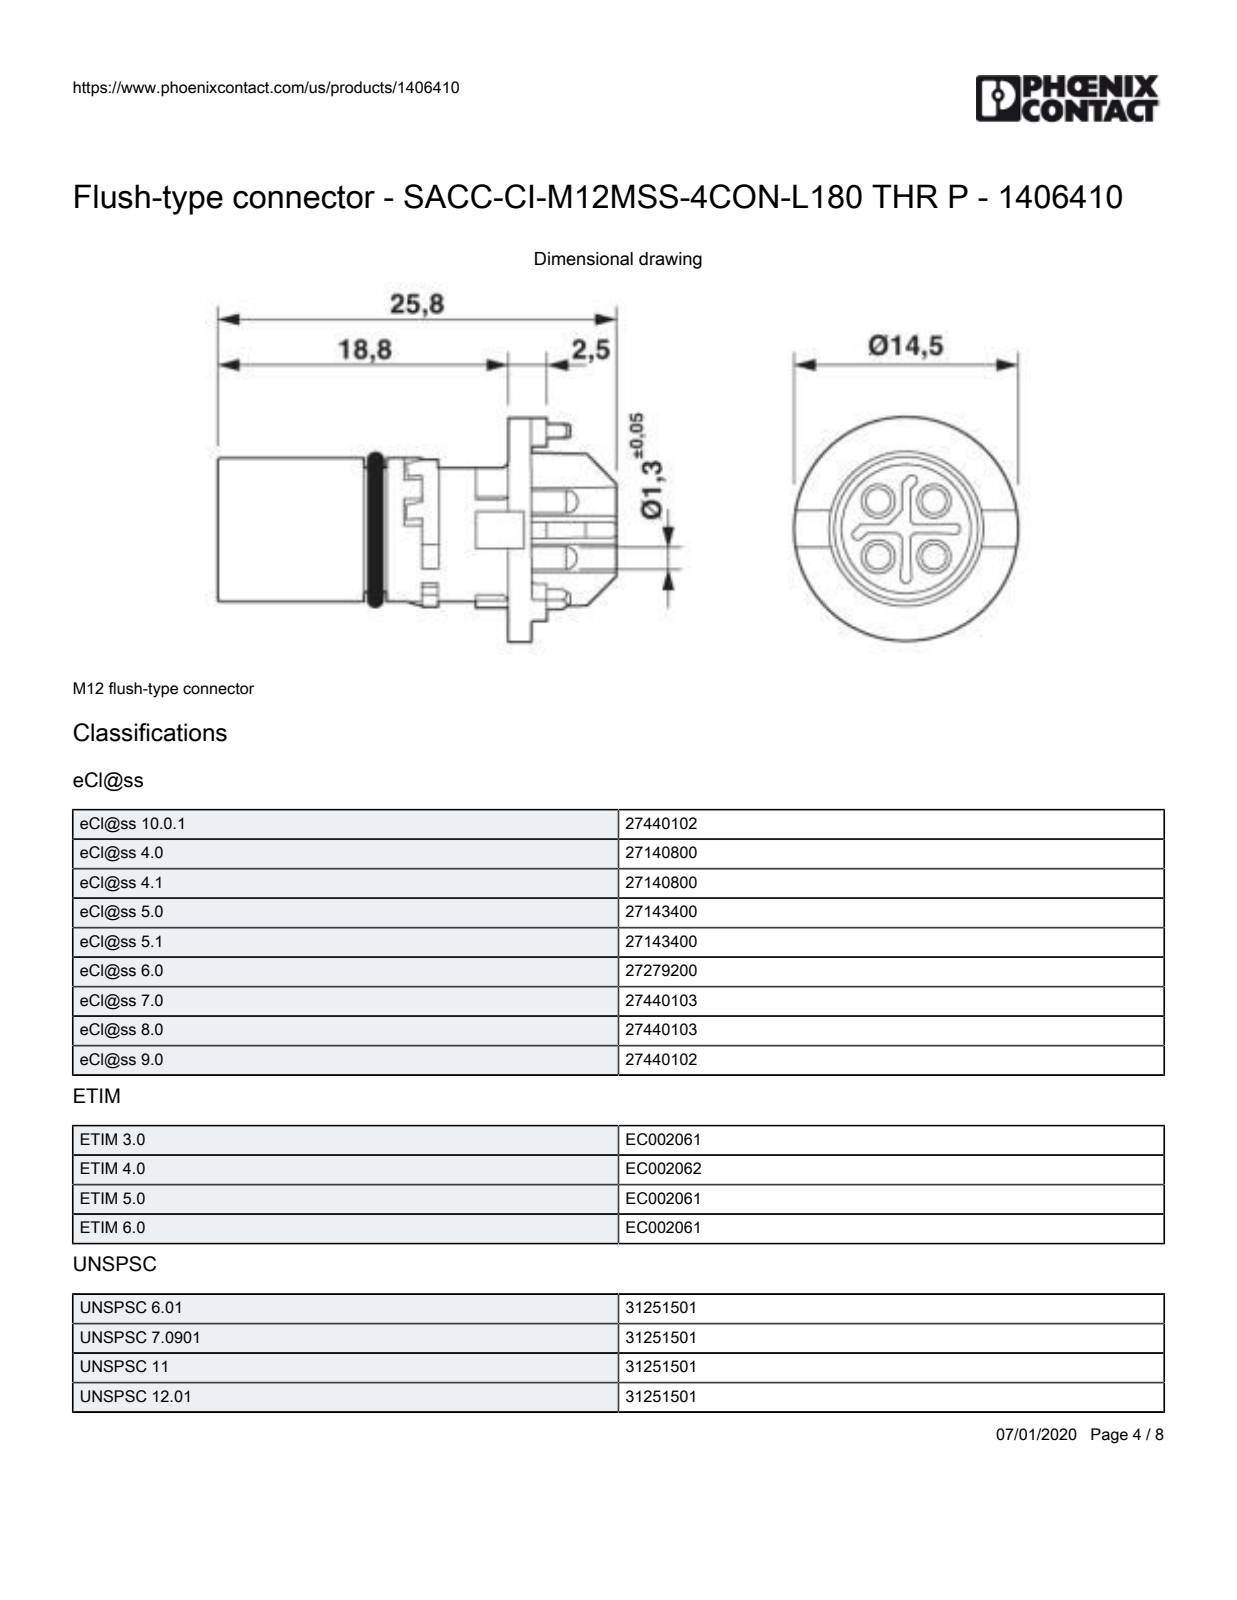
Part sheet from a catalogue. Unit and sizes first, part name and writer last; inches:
Units: inches
Overall size (bounding box): 1.016 × 0.571 × 0.571
Round holes (diameter × count): ⌀0.041 ×1, ⌀0.329 ×1
Round bosses / shafts (diameter × count): ⌀0.085 ×4, ⌀0.059 ×4, ⌀0.051 ×4, ⌀0.571 ×1, ⌀0.366 ×1, ⌀0.315 ×1, ⌀0.091 ×1
Partial cylindrical surfaces — rounded edges, fillets, slot ends (radius × count): R0.008 ×45, R0.02 ×11, R0.176 ×5, R0.188 ×5, R0.004 ×4, R0.014 ×4, R0.061 ×4, R0.016 ×3
Main face-to-face distances: 0.059, 0.031, 0.039, 0.022, 0.177, 0.138, 0.189, 0.368, 0.028, 0.041
Hole centre spacings: 0.139
Volume: 0.076 in³ · Surface area: 3.139 in²
Bodies: 1 solid, 606 faces (335 planar, 159 cylindrical, 112 other)
Part name (STEP PRODUCT): 1406410
STEP written by: PRO/ENGINEER BY PARAMETRIC TECHNOLOGY CORPORATION, 2012480 (AUTOMOTIVE_DESIGN)
